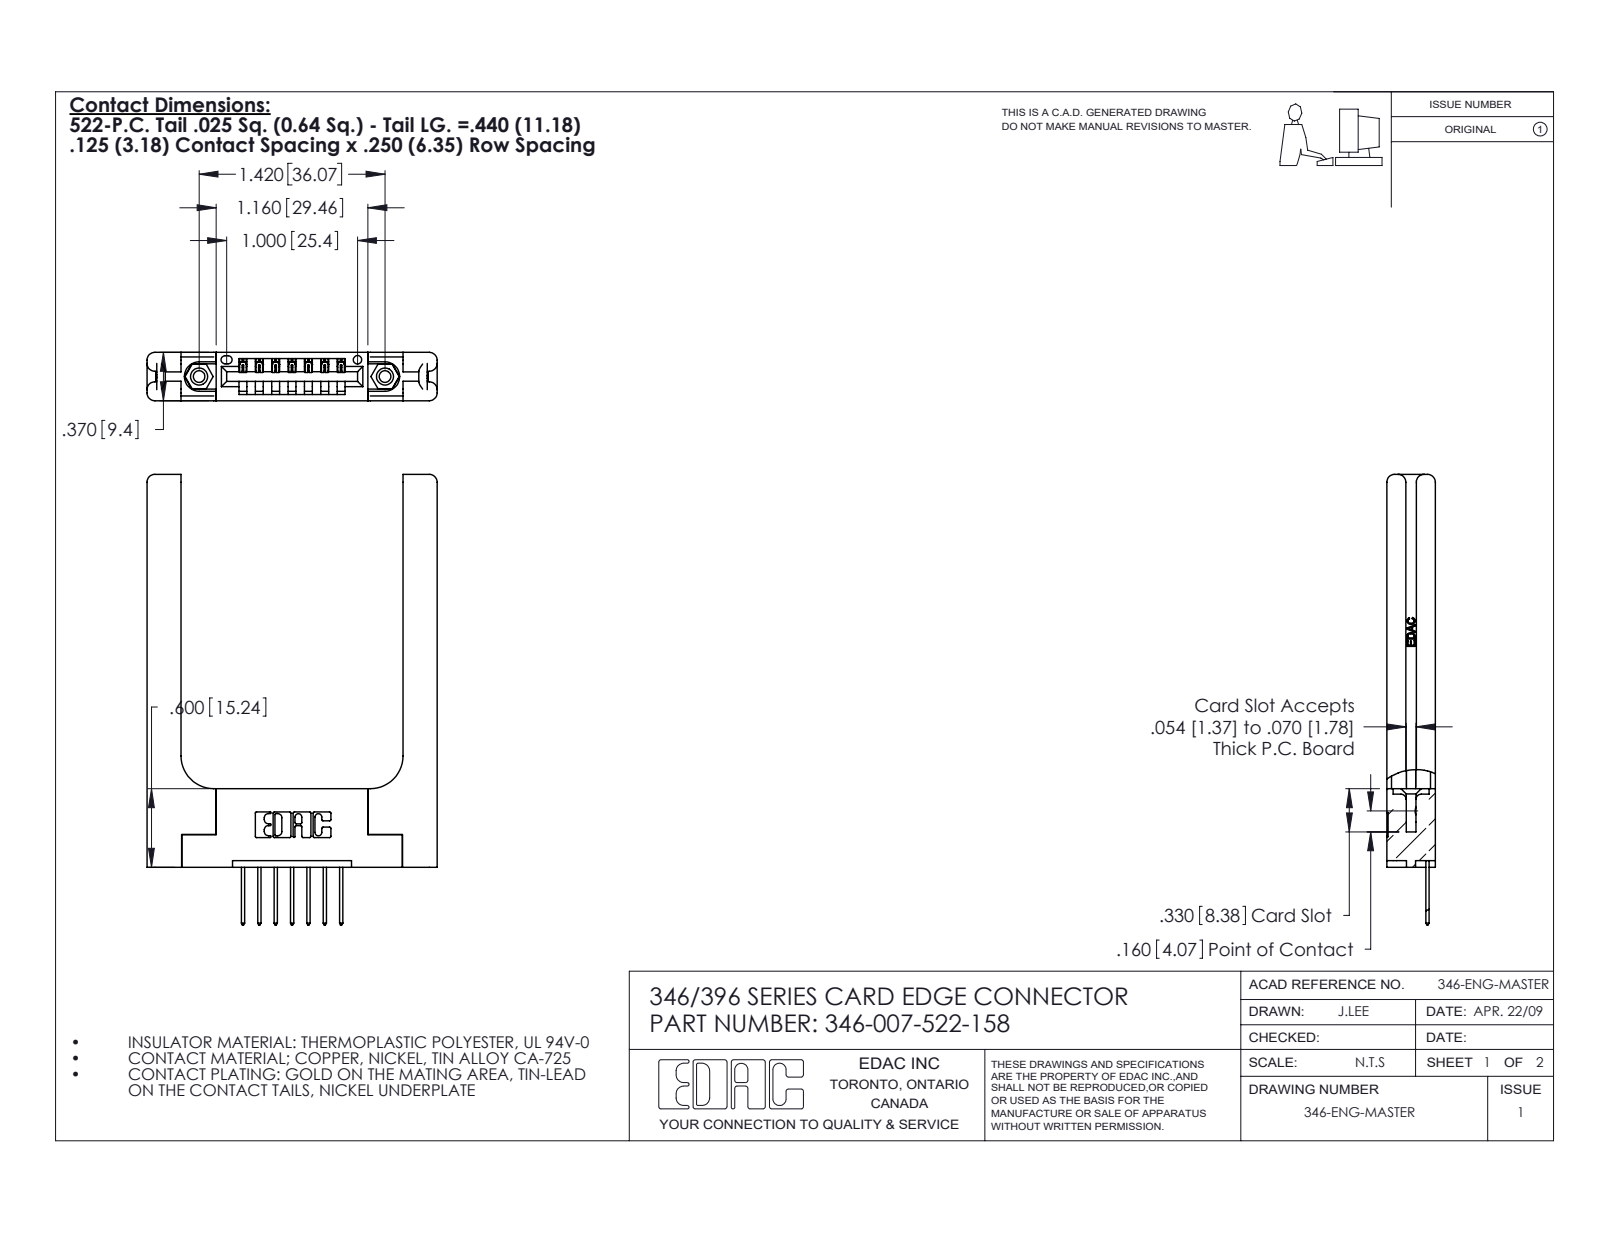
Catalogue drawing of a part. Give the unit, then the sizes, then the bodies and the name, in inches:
Units: inches
Overall size (bounding box): 3.44 × 2.216 × 0.37
Round holes (diameter × count): ⌀0.089 ×2, ⌀0.125 ×2, ⌀0.156 ×2, ⌀0.064 ×1
Round bosses / shafts (diameter × count): ⌀0.155 ×2
Partial cylindrical surfaces — rounded edges, fillets, slot ends (radius × count): R0.01 ×22, R0.06 ×16, R0.006 ×14, R0.01 ×14, R0.007 ×6, R0.031 ×6, R0.026 ×3, R0.03 ×2
Main face-to-face distances: 0.37, 0.15, 0.22, 0.072, 0.148, 0.25, 1.696, 0.048, 0.322, 0.102
Hole centre spacings: 0.246, 1.217, 1.42
Volume: 0.772 in³ · Surface area: 17.45 in²
Bodies: 12 solids, 798 faces (518 planar, 220 cylindrical, 60 other)
Part name (STEP PRODUCT): 345-292-001_345-293-122; 346 Part_Flush Mounting Lugs - 0.156 Dia-TH; 346-007-522-158; 345-250-001_345-250-001-102 (+1 more)
STEP written by: SolidWorks 2020 (CONFIG_CONTROL_DESIGN)
